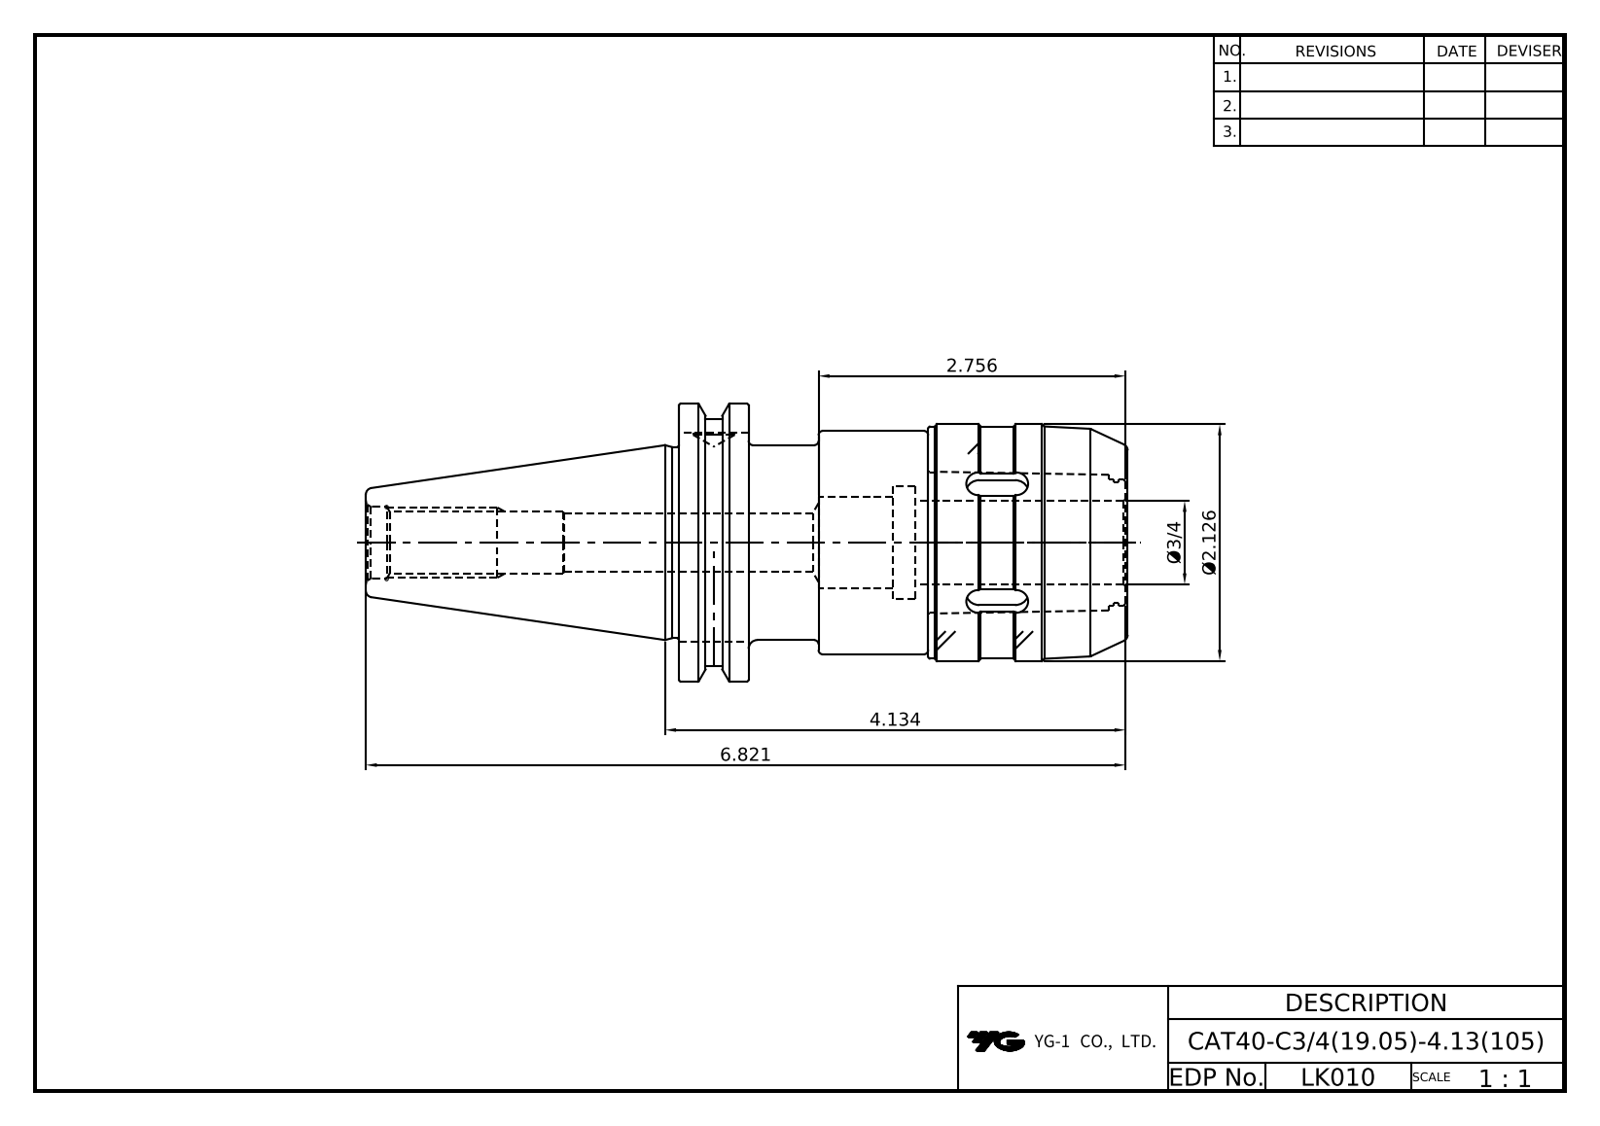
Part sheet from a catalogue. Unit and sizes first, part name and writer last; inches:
Units: inches
Overall size (bounding box): 6.837 × 2.5 × 2.405
Round holes (diameter × count): ⌀0.375 ×1, ⌀0.512 ×1, ⌀0.527 ×1, ⌀0.642 ×1, ⌀0.75 ×1, ⌀0.827 ×1, ⌀1.008 ×1, ⌀1.539 ×1, ⌀1.614 ×1
Round bosses / shafts (diameter × count): ⌀2.5 ×1, ⌀2.217 ×1, ⌀2.126 ×1, ⌀2.087 ×1, ⌀2.008 ×1, ⌀1.75 ×1, ⌀1.717 ×1, ⌀1.138 ×1
Partial cylindrical surfaces — rounded edges, fillets, slot ends (radius × count): R0.118 ×6
Main face-to-face distances: 2.233, 0.625, 1.608, 4.005, 3.38, 1.772, 4.025, 3.4, 1.791, 0.02
Volume: 14.51 in³ · Surface area: 81.11 in²
Bodies: 2 solids, 159 faces (58 planar, 43 cylindrical, 58 other)
Part name (STEP PRODUCT): CAT40-C19.05-104.9; C20-CAP
STEP written by: Autodesk Inventor 2020 (AUTOMOTIVE_DESIGN)
